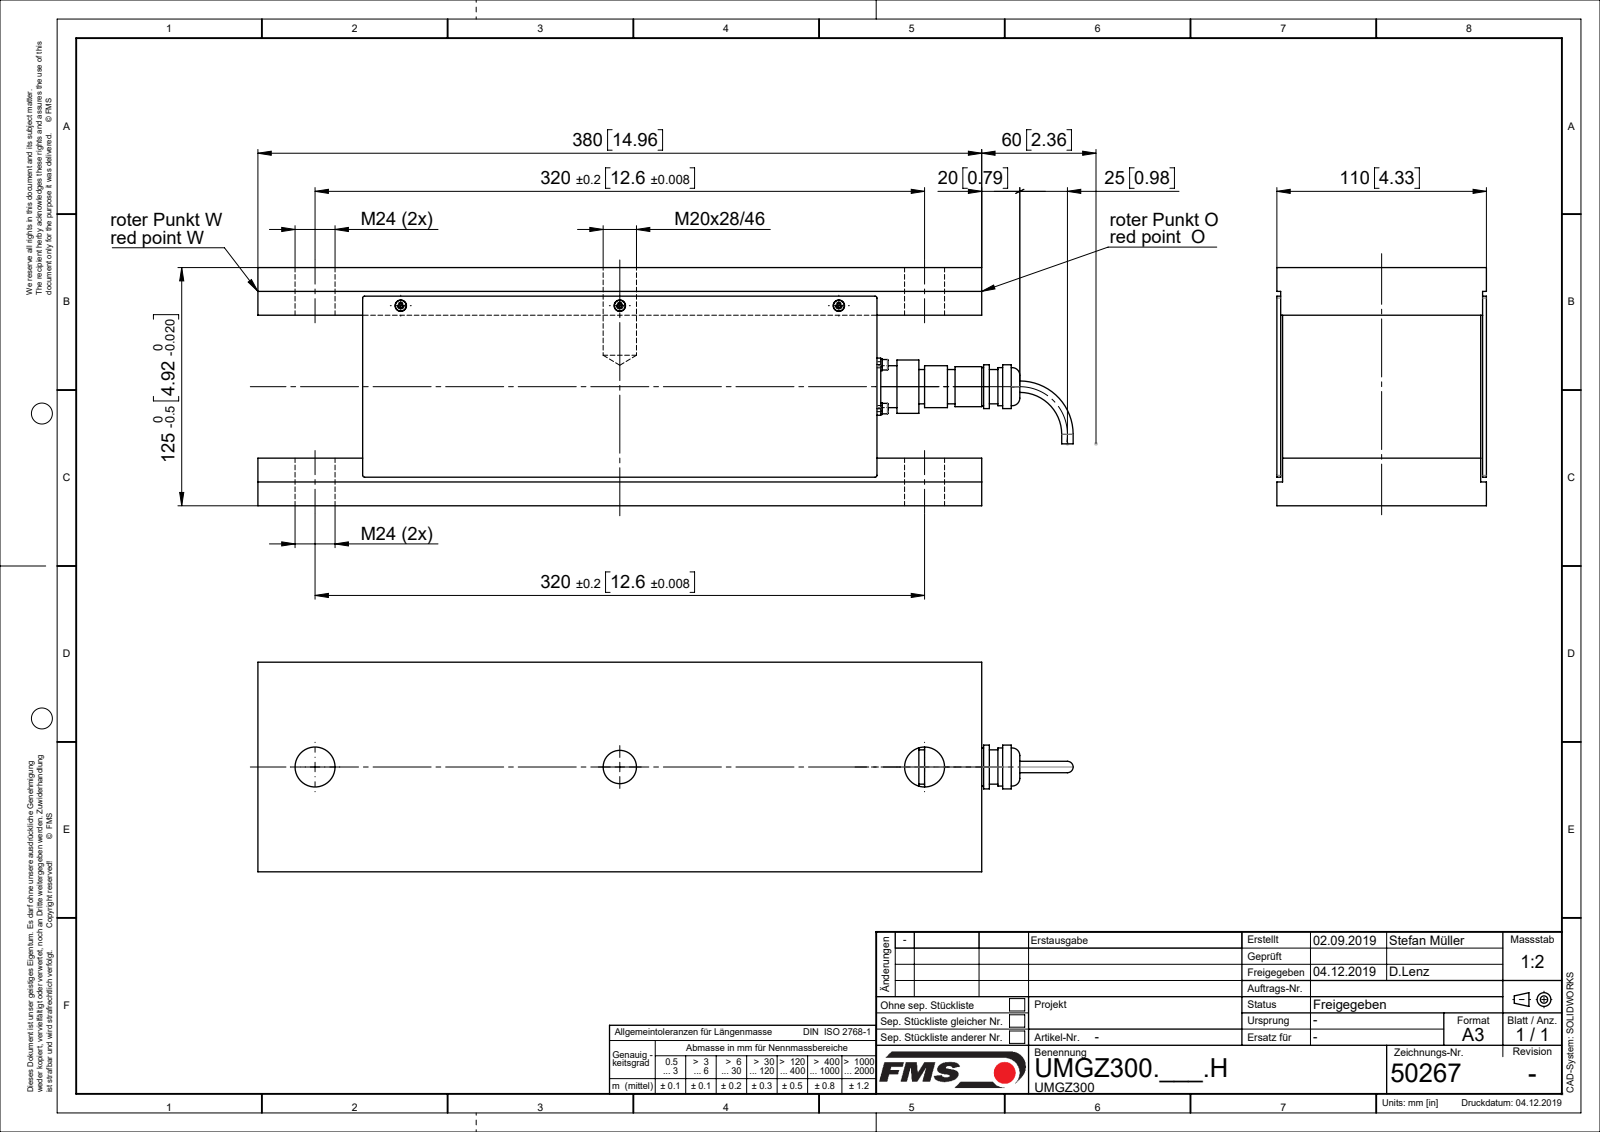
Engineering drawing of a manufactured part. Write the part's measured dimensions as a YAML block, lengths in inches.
part_name: "U50267; U4996704; TEIL1; U48466 (+5 more)"
step_written_by: "Mechanical Desktop 2007 (CONFIG_CONTROL_DESIGN)"
units: inches
bodies: {solids: 18, faces: 371, planar: 133, cylindrical: 158, other: 80}
overall_size: [16.85, 4.921, 4.331]
volume: 258.1
surface_area: 529.3
round_holes:
  - {diameter: 0.102, count: 7}
  - {diameter: 0.126, count: 4}
  - {diameter: 0.142, count: 3}
  - {diameter: 0.236, count: 3}
  - {diameter: 0.837, count: 2}
  - {diameter: 0.698, count: 1}
round_bosses_or_shafts:
  - {diameter: 0.118, count: 7}
  - {diameter: 0.244, count: 4}
  - {diameter: 0.217, count: 4}
  - {diameter: 0.098, count: 4}
  - {diameter: 1.102, count: 1}
  - {diameter: 0.906, count: 1}
  - {diameter: 0.866, count: 1}
  - {diameter: 0.827, count: 1}
partial_cylinders:
  - {radius: 0.157, count: 4}
face_to_face_distances: [0.079, 4.252, 0.118, 0.039, 4.213, 4.134, 4.921, 4.331, 4.173, 4.094]
hole_center_spacings: [0.906, 1.281, 4.528, 6.299, 9.055, 12.598]
